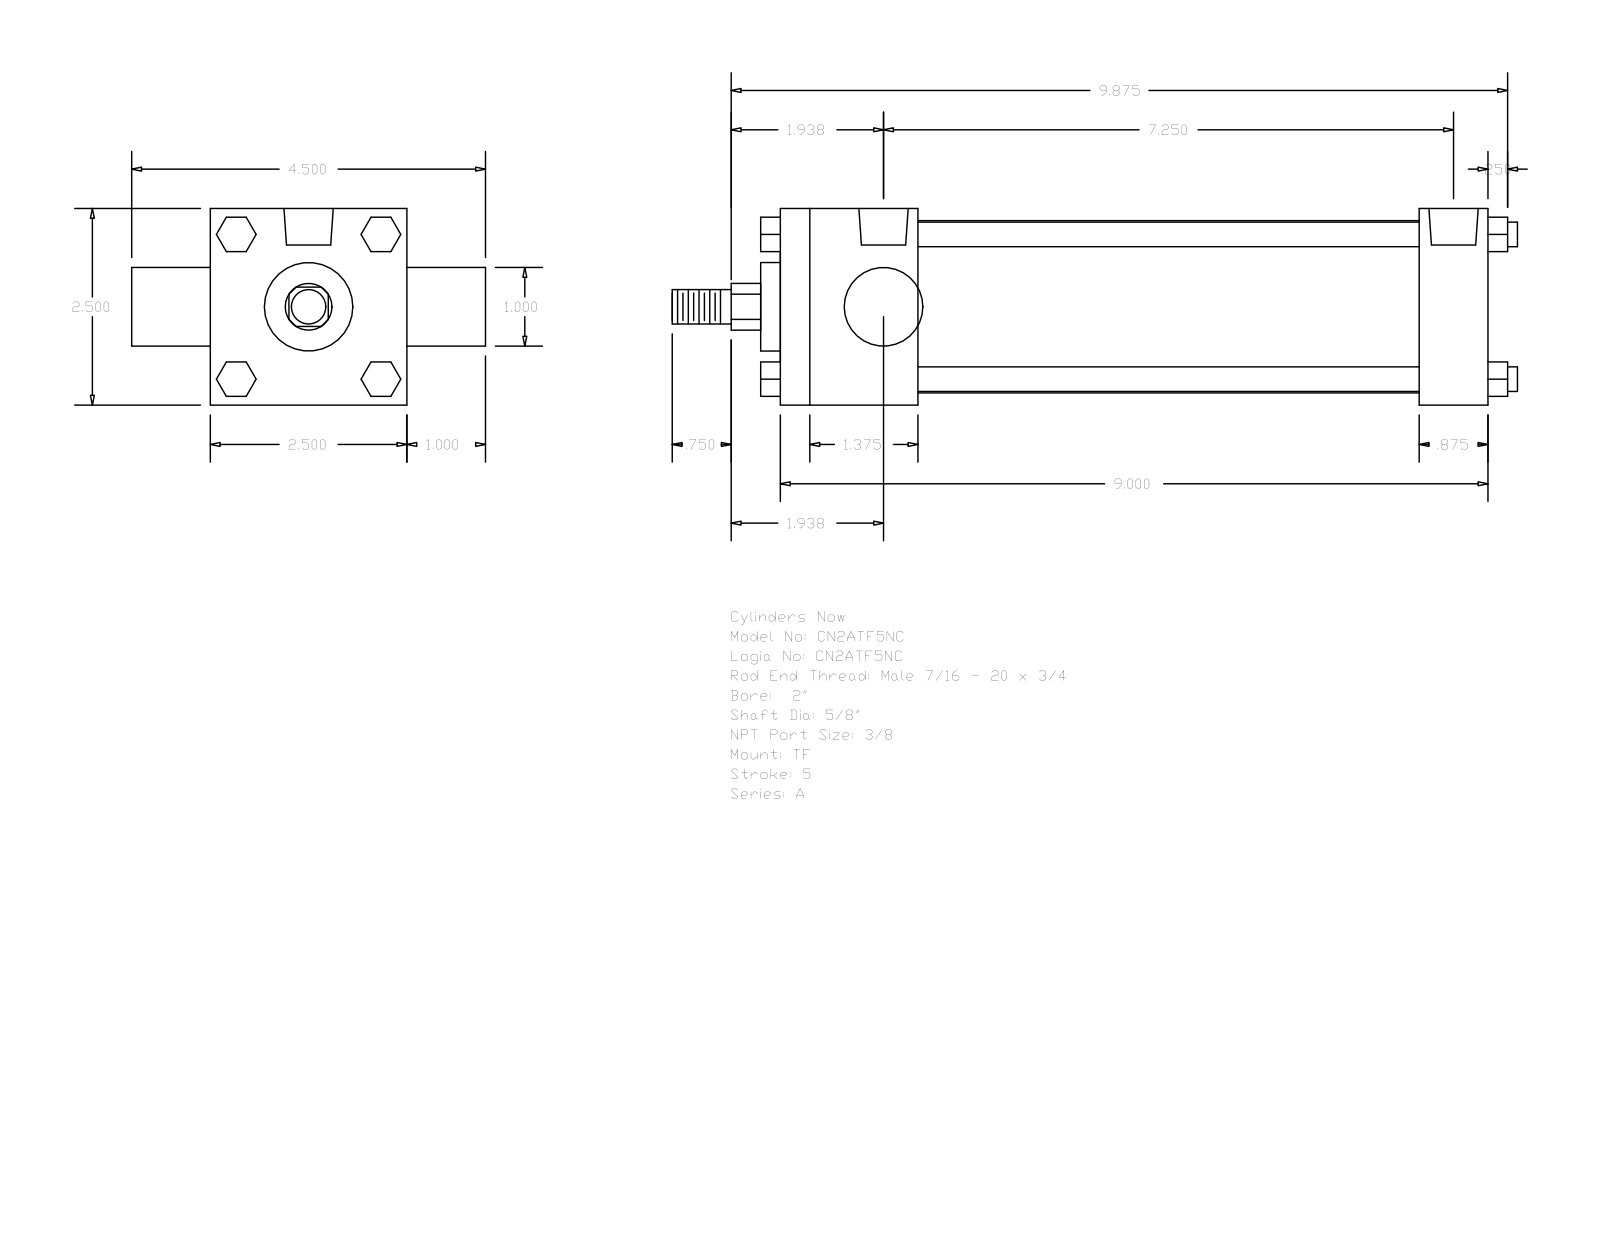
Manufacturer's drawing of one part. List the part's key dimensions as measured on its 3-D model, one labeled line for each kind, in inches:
Part name (STEP PRODUCT): A_TF__0200_0.625
STEP written by: GSSL Pune (CONFIG_CONTROL_DESIGN)
Units: inches
Bodies: 0 solids, 120 faces (92 planar, 28 cylindrical, 0 other)
Overall size (bounding box): 10.75 × 4.5 × 2.5
Round holes (diameter × count): ⌀0.219 ×3, ⌀0.627 ×2
Round bosses / shafts (diameter × count): ⌀0.313 ×4, ⌀2.19 ×1, ⌀1.125 ×1, ⌀1 ×1, ⌀0.625 ×1, ⌀0.437 ×1
Partial cylindrical surfaces — rounded edges, fillets, slot ends (radius × count): R0.297 ×1
Main face-to-face distances: 2.5, 9, 1.75, 8.125, 6.375, 7.25, 0.875, 1, 3.5, 0.25
Hole centre spacings: 0.156, 0.157, 6.937, 7.093, 7.094, 7.25
